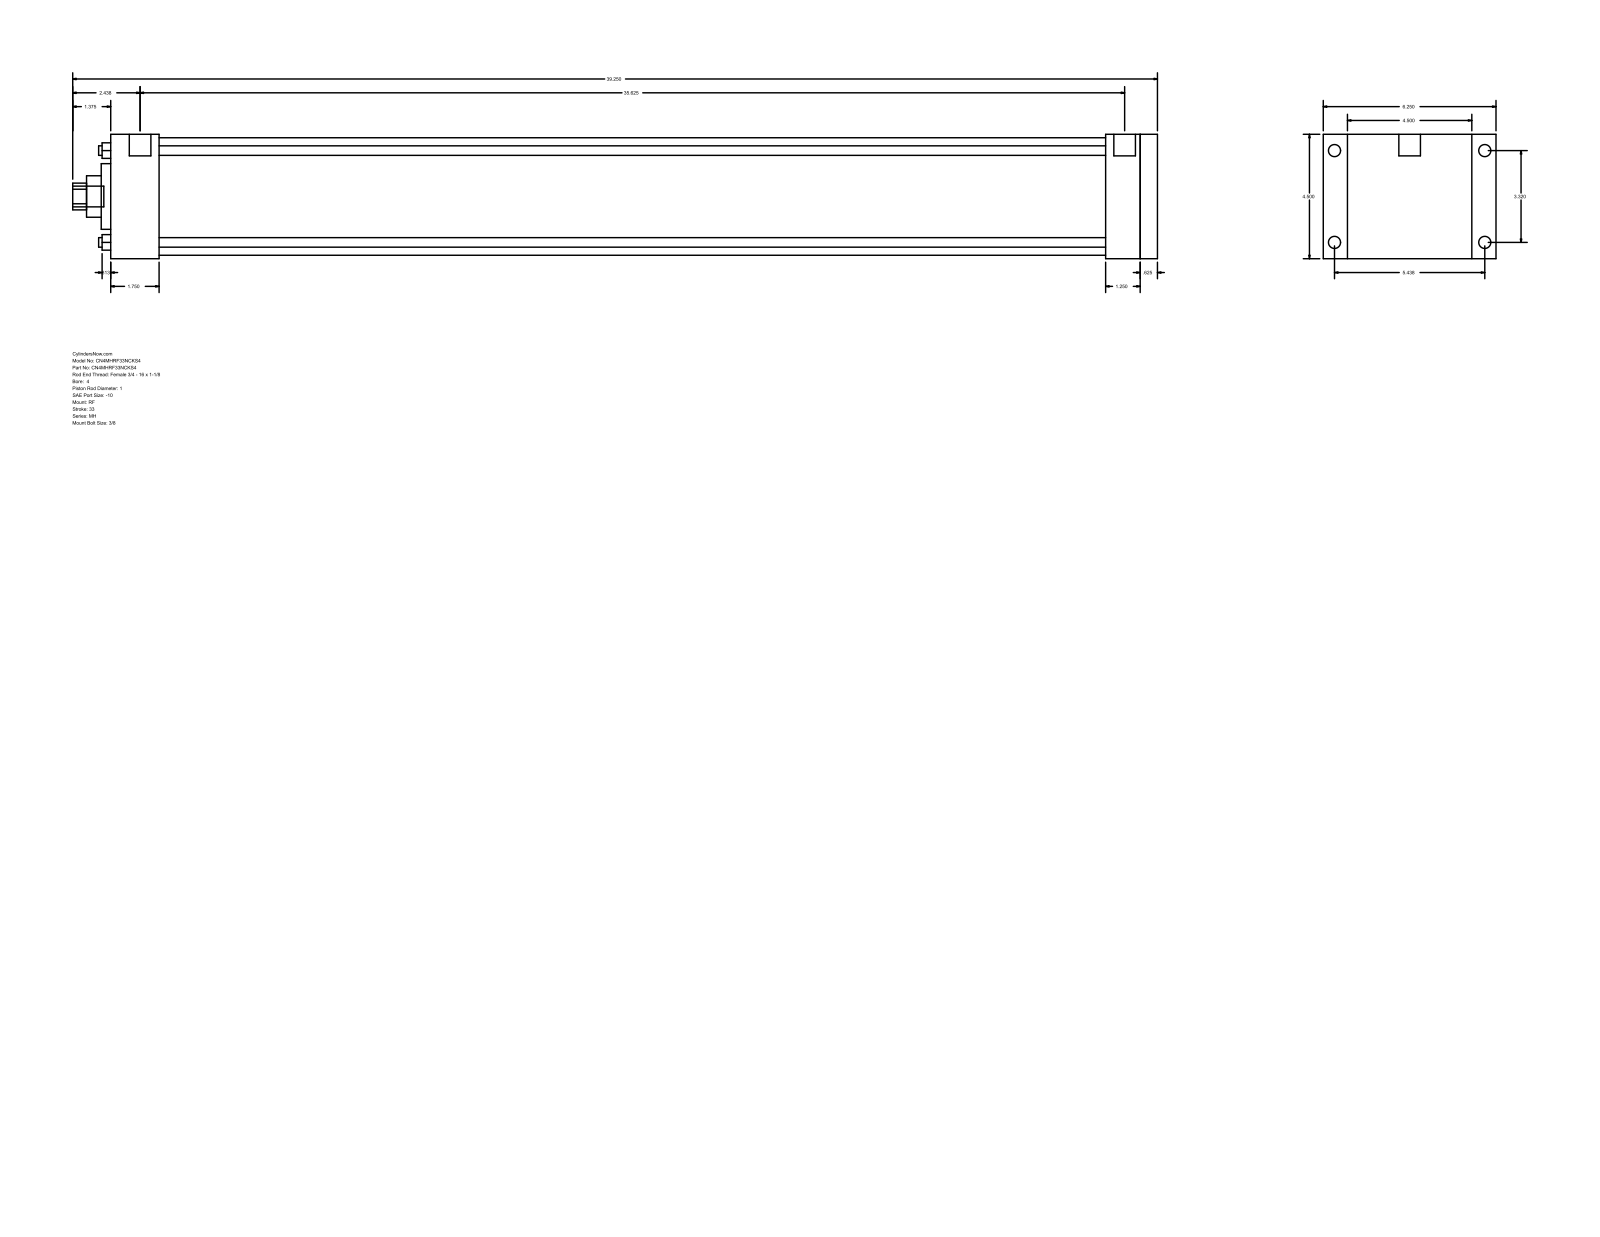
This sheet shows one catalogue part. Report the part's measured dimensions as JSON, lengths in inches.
{"part_name": "MH_RF__0400_1", "step_written_by": "GSSL Pune (CONFIG_CONTROL_DESIGN)", "units": "inches", "bodies": {"solids": 0, "faces": 94, "planar": 65, "cylindrical": 29, "other": 0}, "overall_size": [39.25, 6.25, 4.5], "round_holes": [[0.345, 4], [1, 1], [1.5, 1], [2.375, 1], [4.25, 1]], "round_bosses_or_shafts": [[0.438, 4], [0.344, 4], [0.781, 2], [0.75, 1]], "partial_cylinders_radius": [[0.484, 1]], "face_to_face_distances": [4.5, 37.875, 0.625, 37.25, 1.75, 35.5, 36.125, 36, 34.25, 1.25], "hole_center_spacings": [2.347, 3.32, 4.695]}
